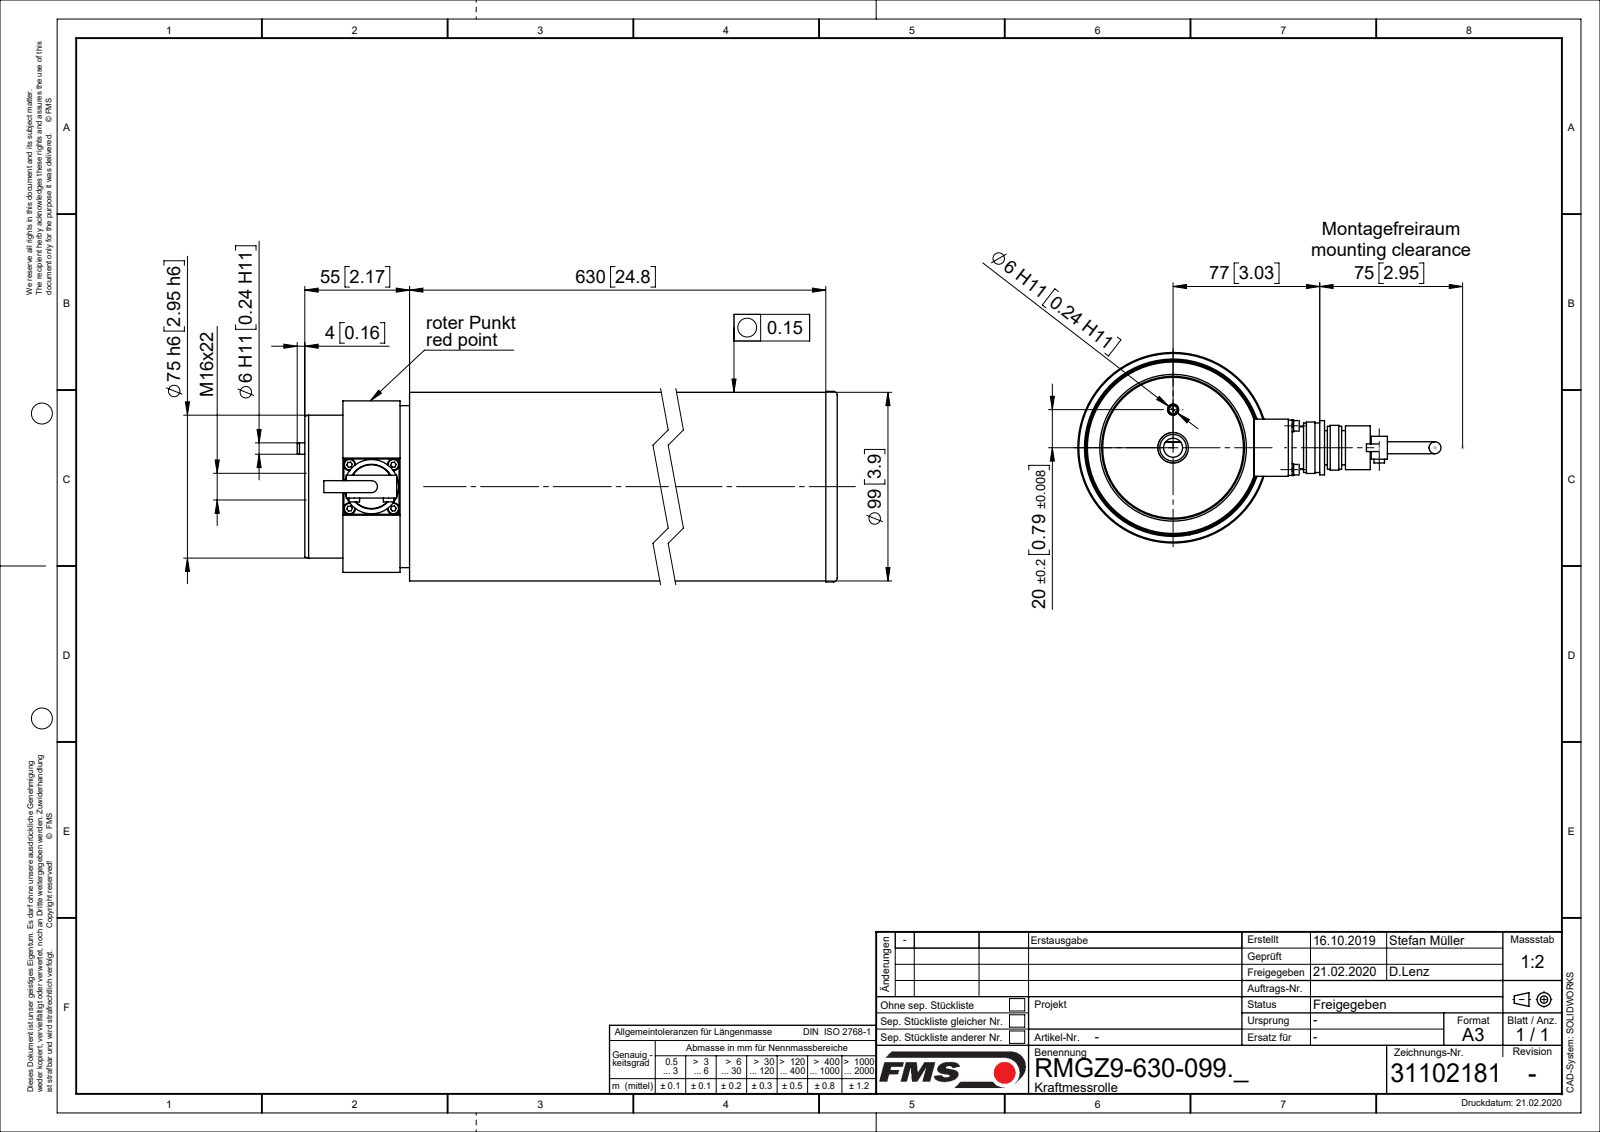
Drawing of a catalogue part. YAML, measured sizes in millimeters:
part_name: "47726-04_stp_01; Federringe_DIN127A_M03; 130509-4_01; 130507.5_01 (+8 more)"
step_written_by: "SolidWorks 2018 (CONFIG_CONTROL_DESIGN)"
units: millimeters
bodies: {solids: 31, faces: 570, planar: 162, cylindrical: 234, other: 174}
overall_size: [695, 190.65, 100]
volume: 2236000
surface_area: 630378
round_holes:
  - {diameter: 2.5, count: 4}
  - {diameter: 3.1, count: 4}
  - {diameter: 3.4, count: 4}
  - {diameter: 3.3, count: 1}
  - {diameter: 5, count: 1}
  - {diameter: 6, count: 1}
  - {diameter: 10, count: 1}
  - {diameter: 12, count: 1}
  - {diameter: 14, count: 1}
  - {diameter: 22, count: 1}
  - {diameter: 23, count: 1}
  - {diameter: 26, count: 1}
round_bosses_or_shafts:
  - {diameter: 5.5, count: 6}
  - {diameter: 6.2, count: 4}
  - {diameter: 3, count: 4}
  - {diameter: 2.5, count: 4}
  - {diameter: 100, count: 1}
  - {diameter: 99, count: 1}
  - {diameter: 91, count: 1}
  - {diameter: 90, count: 1}
partial_cylinders:
  - {radius: 11, count: 4}
  - {radius: 4.25, count: 2}
  - {radius: 17.5, count: 1}
face_to_face_distances: [50, 32, 156, 10, 2, 225, 35, 381, 414, 524]
hole_center_spacings: [16.26, 23, 32.53, 20]
